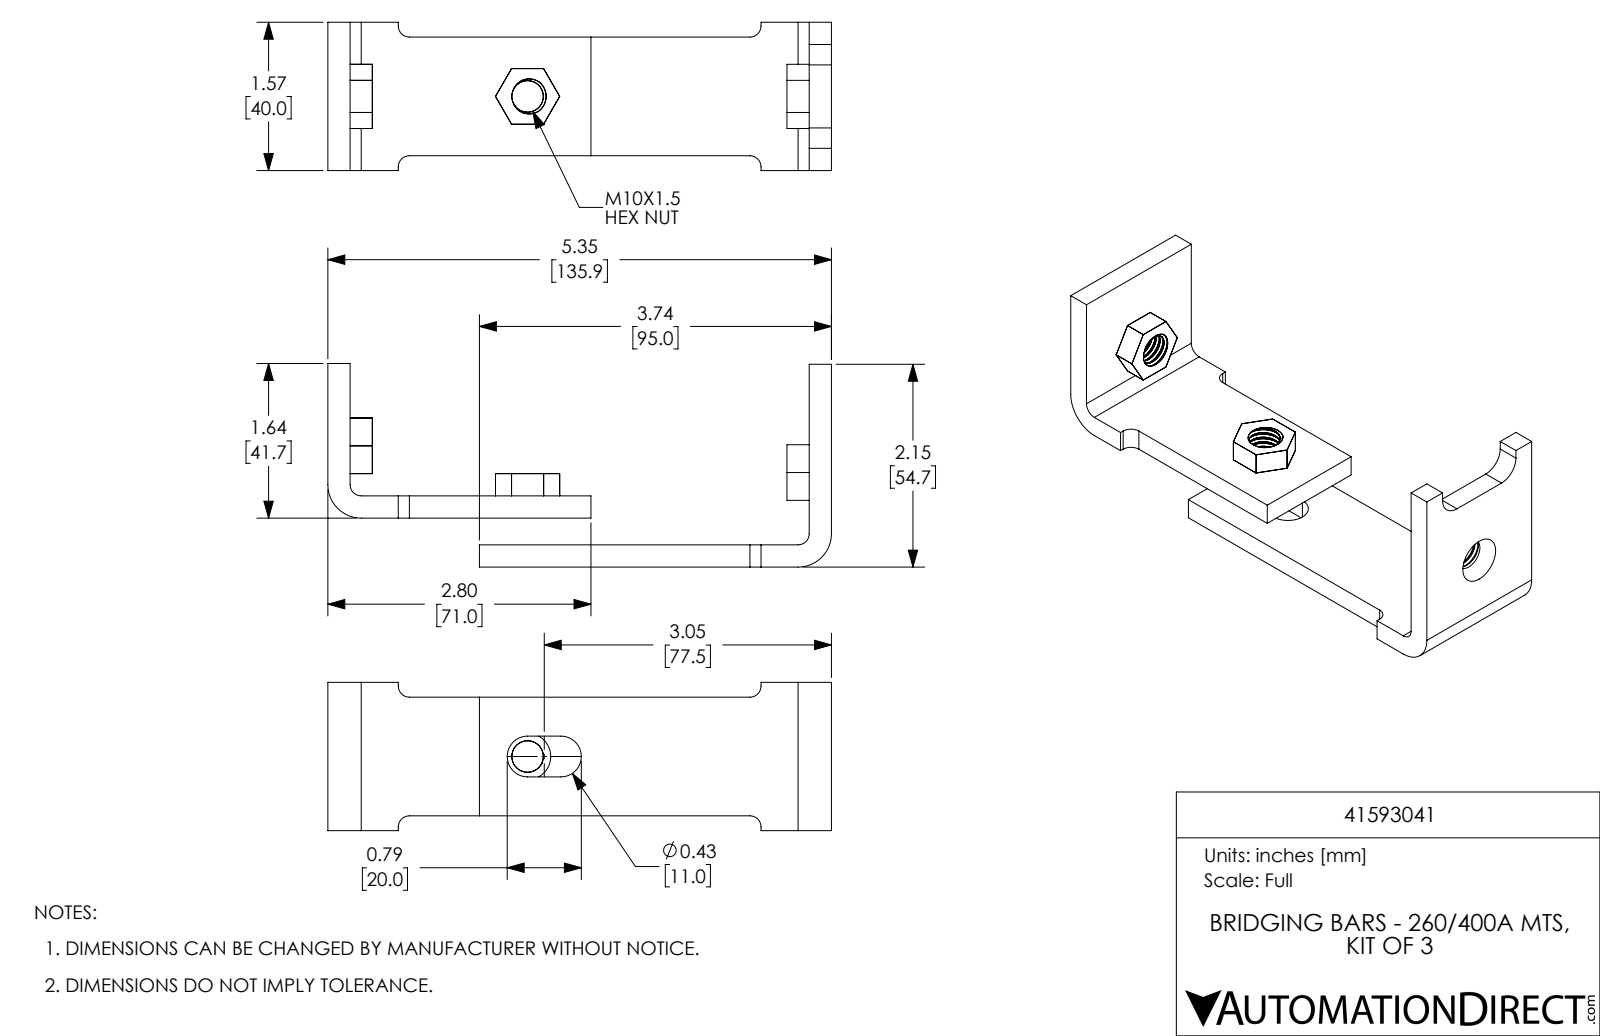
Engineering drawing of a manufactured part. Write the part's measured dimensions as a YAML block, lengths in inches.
part_name: "41593041"
step_written_by: "SolidWorks 2017 (AUTOMOTIVE_DESIGN)"
units: inches
bodies: {solids: 7, faces: 233, planar: 80, cylindrical: 143, other: 10}
overall_size: [5.35, 2.162, 1.575]
volume: 3.208
surface_area: 40.43
round_holes:
  - {diameter: 0.335, count: 3}
  - {diameter: 0.394, count: 3}
  - {diameter: 0.492, count: 3}
round_bosses_or_shafts:
  - {diameter: 0.512, count: 3}
partial_cylinders:
  - {radius: 0.118, count: 6}
  - {radius: 0.217, count: 4}
  - {radius: 0.354, count: 2}
face_to_face_distances: [0.236, 0.52, 5.114, 0.756, 0.284, 0.157, 4.878, 1.417, 5.35, 0.591]
hole_center_spacings: [0.284]
